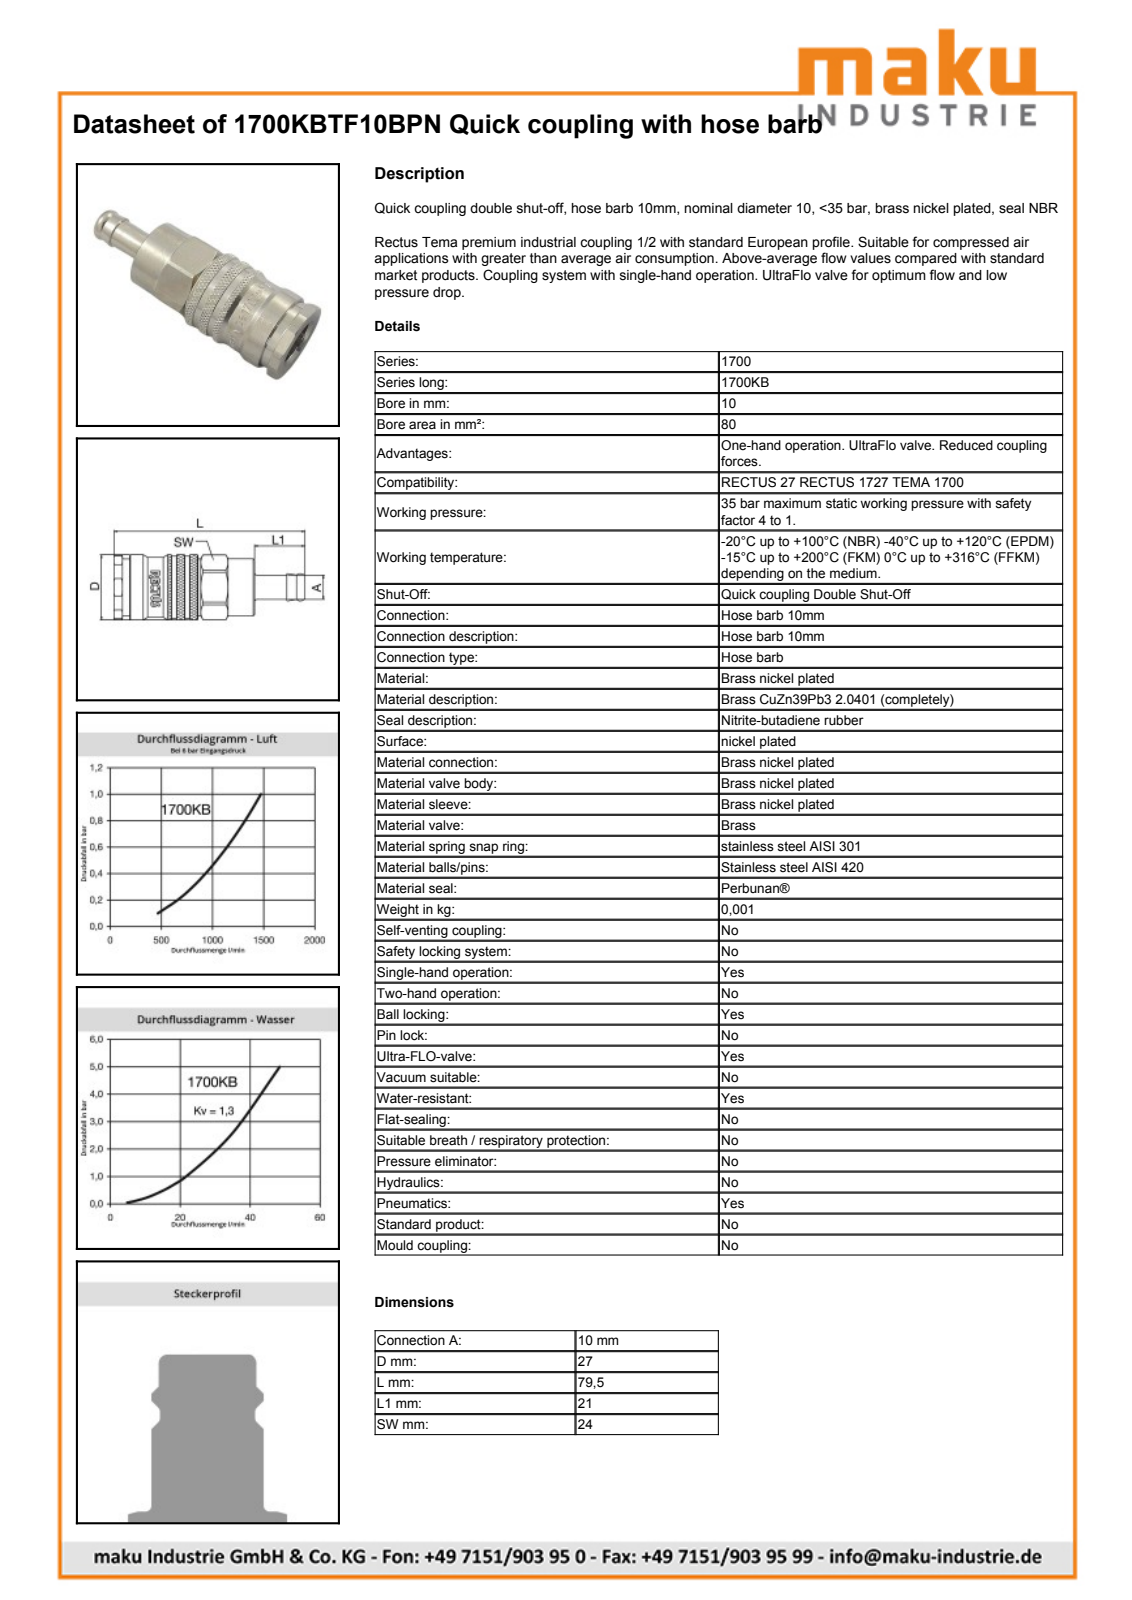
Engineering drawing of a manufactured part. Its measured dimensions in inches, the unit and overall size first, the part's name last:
Units: inches
Overall size (bounding box): 3.135 × 1.065 × 1.055
Round holes (diameter × count): ⌀0.793 ×1, ⌀0.835 ×1, ⌀0.843 ×1, ⌀0.886 ×1, ⌀0.937 ×1, ⌀0.945 ×1
Round bosses / shafts (diameter × count): ⌀1.055 ×1, ⌀1.024 ×1, ⌀0.984 ×1, ⌀0.933 ×1, ⌀0.839 ×1, ⌀0.827 ×1, ⌀0.826 ×1, ⌀0.787 ×1
Partial cylindrical surfaces — rounded edges, fillets, slot ends (radius × count): R0.488 ×1, R0.531 ×1, R0.533 ×1
Main face-to-face distances: 0.945, 2.309, 0.039, 0.984, 1.206, 1.102, 0.258, 0.948, 2.051, 3.135
Volume: 1.826 in³ · Surface area: 18.96 in²
Bodies: 2 solids, 664 faces (196 planar, 93 cylindrical, 375 other)
Part name (STEP PRODUCT): D103703
STEP written by: Autodesk Inventor 2013 (AUTOMOTIVE_DESIGN)
